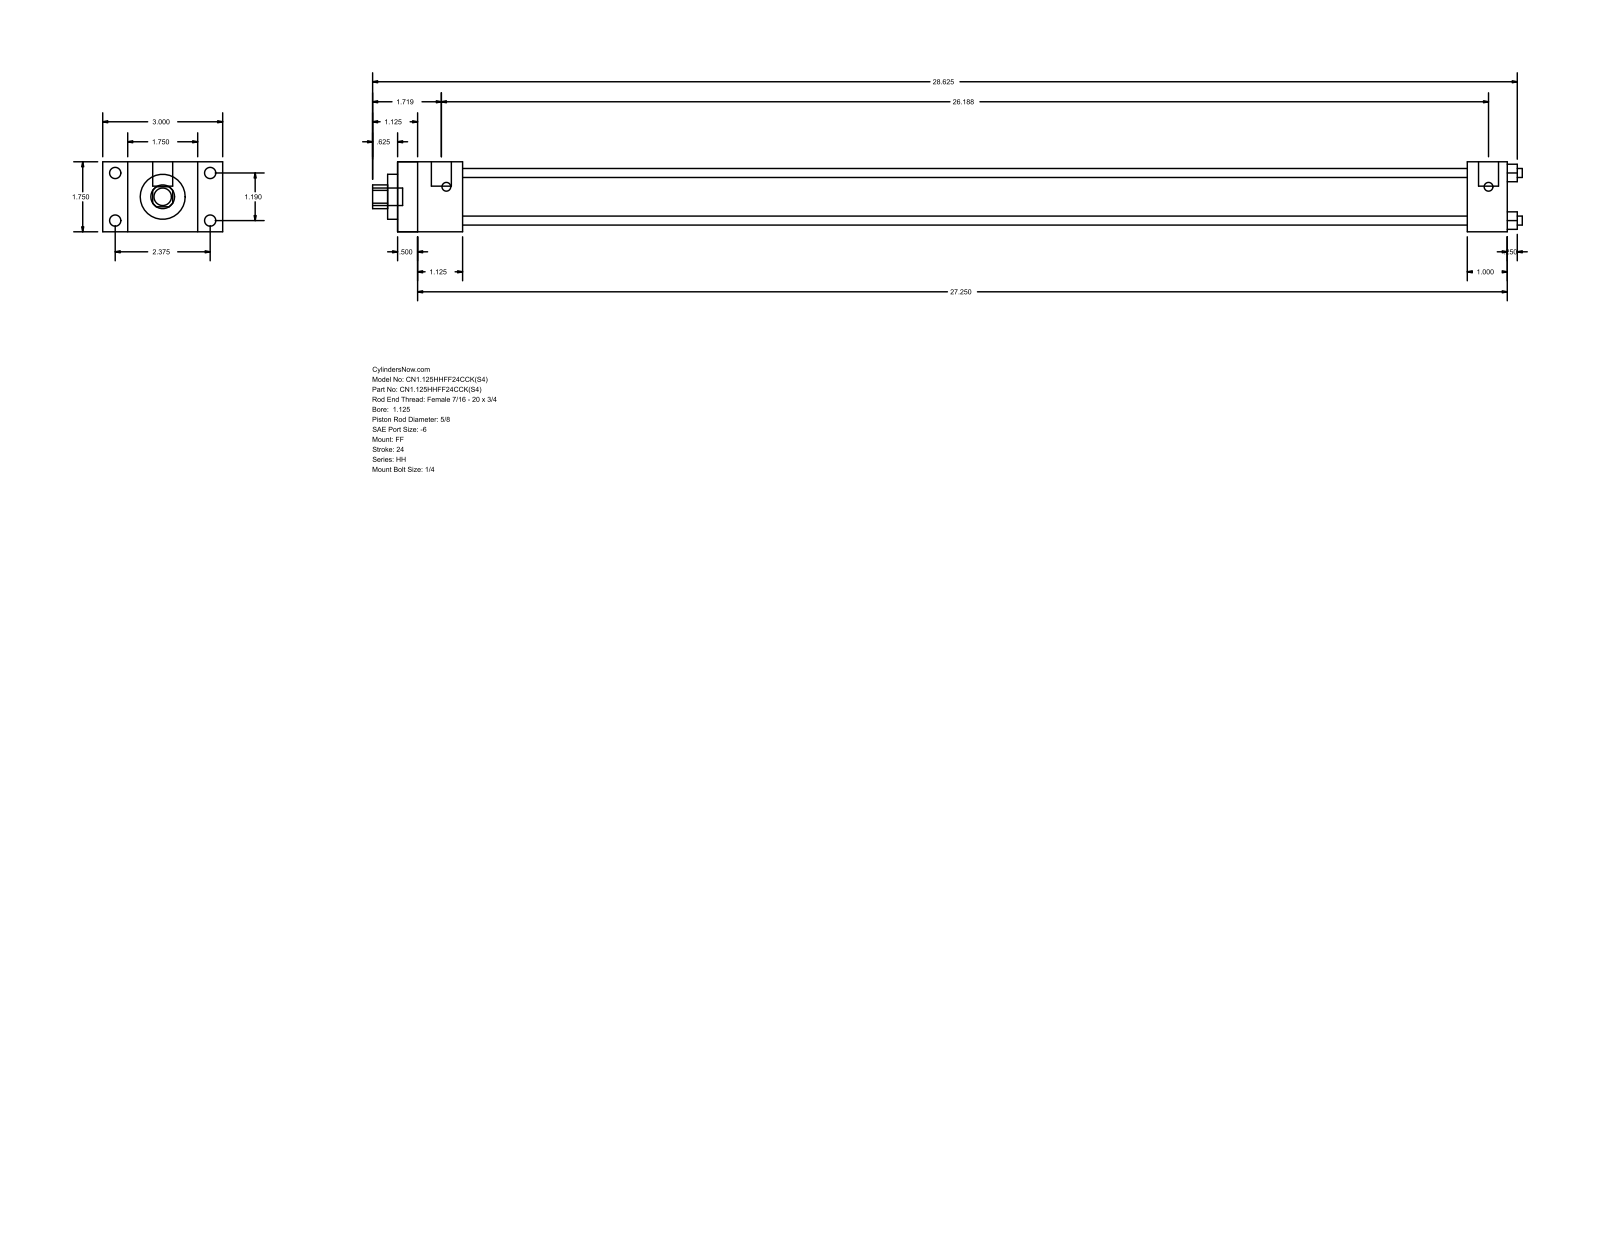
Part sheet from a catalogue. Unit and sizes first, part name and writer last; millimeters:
Units: millimetres
Overall size (bounding box): 730.25 × 76.2 × 44.45
Round holes (diameter × count): ⌀5.71 ×4, ⌀15.88 ×1, ⌀28.57 ×1, ⌀34.92 ×1
Round bosses / shafts (diameter × count): ⌀7.14 ×4, ⌀5.56 ×4, ⌀12.7 ×2, ⌀11.11 ×1
Partial cylindrical surfaces — rounded edges, fillets, slot ends (radius × count): R7.54 ×1
Main face-to-face distances: 44.46, 704.85, 12.69, 692.16, 15.87, 60.33, 28.58, 41.27, 679.45, 666.76
Hole centre spacings: 21.37, 30.22, 42.74
Bodies: 0 solids, 92 faces (64 planar, 28 cylindrical, 0 other)
Part name (STEP PRODUCT): HH_FF__0112_0.625
STEP written by: GSSL Pune (CONFIG_CONTROL_DESIGN)
